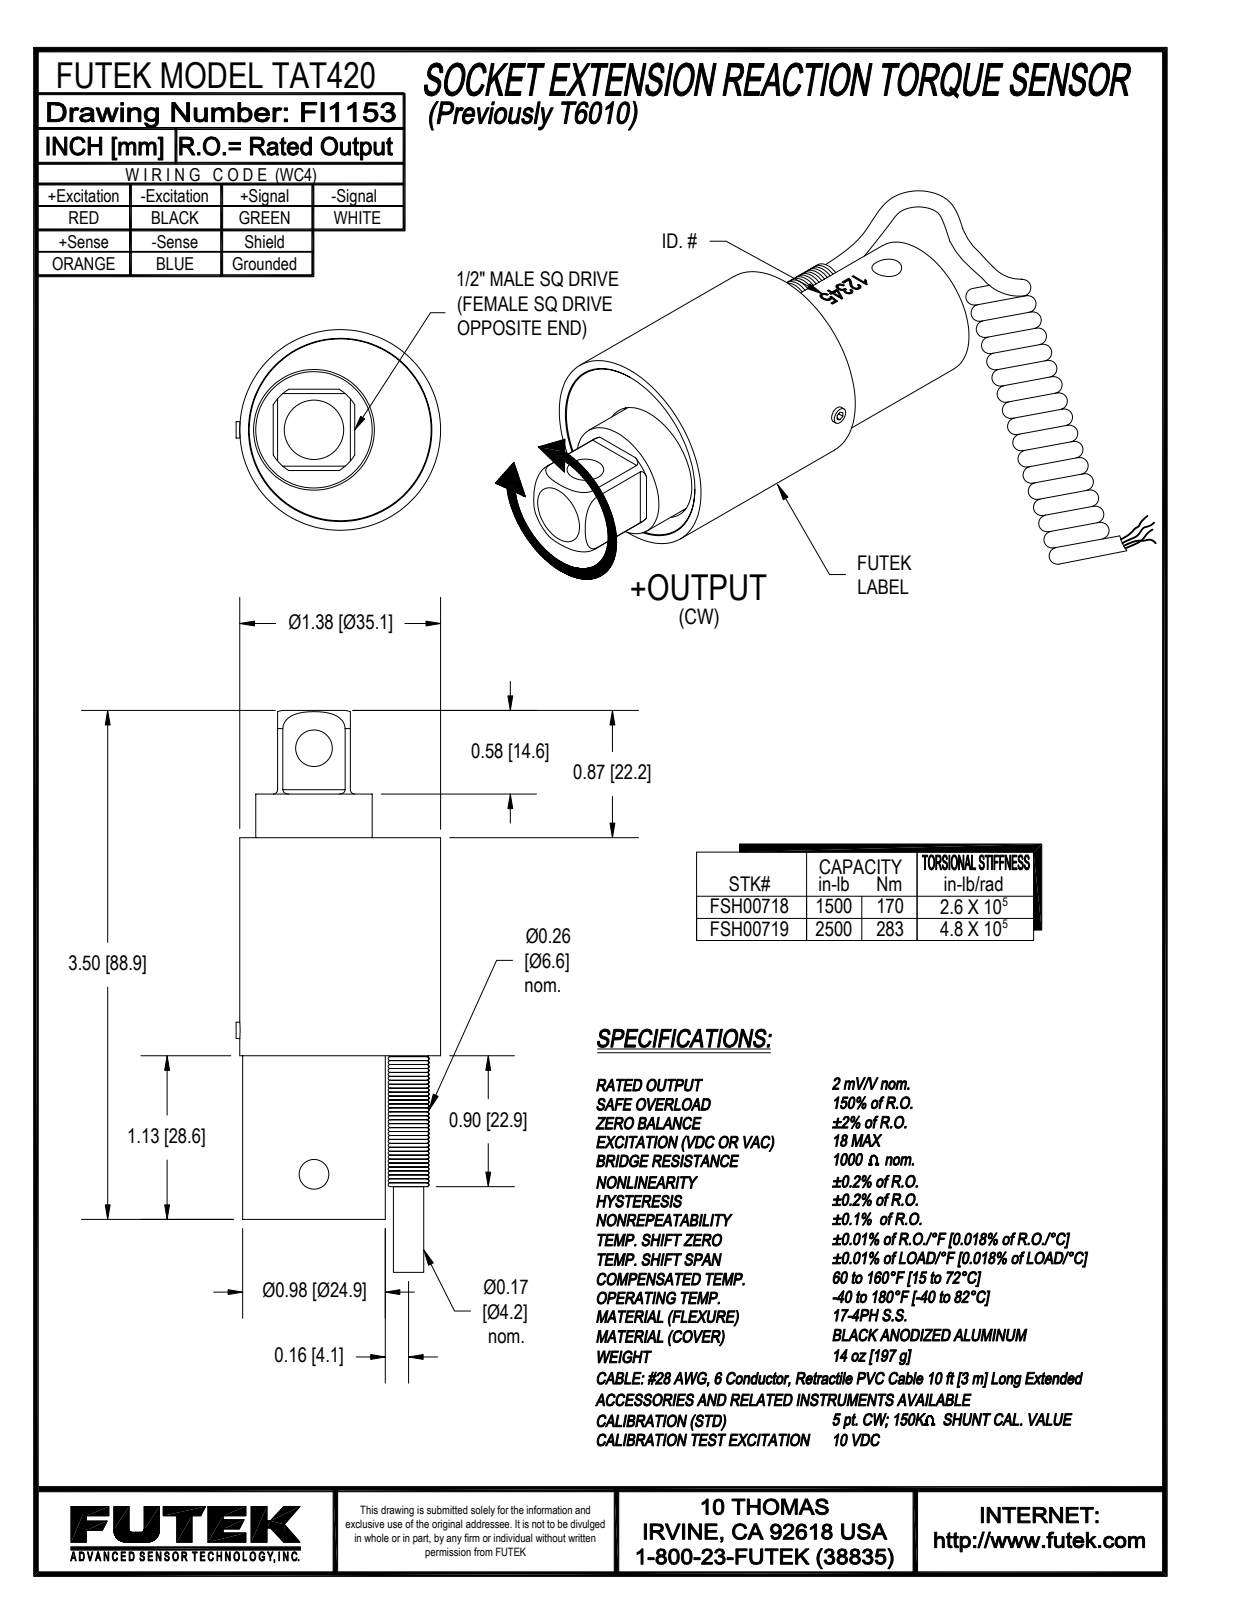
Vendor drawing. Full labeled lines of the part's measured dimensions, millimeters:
Part name (STEP PRODUCT): TAT420 (SubstituteLevelofDetail1); TAT420_Substitute_1
STEP written by: Autodesk Inventor 2011 (AUTOMOTIVE_DESIGN)
Units: millimetres
Bodies: 2 solids, 101 faces (33 planar, 23 cylindrical, 45 other)
Overall size (bounding box): 89.5 × 35.7 × 35.1
Volume: 41 200 mm³ · Surface area: 19 260 mm²
Round holes (diameter × count): ⌀3.3 ×1, ⌀5.1 ×1, ⌀5.2 ×1, ⌀6.4 ×1, ⌀21.1 ×1, ⌀21.8 ×1, ⌀31.2 ×1, ⌀32 ×1
Round bosses / shafts (diameter × count): ⌀35.1 ×1, ⌀31.8 ×1, ⌀24.9 ×1, ⌀21.7 ×1, ⌀20.3 ×1, ⌀5.8 ×1, ⌀2.8 ×1
Partial cylindrical surfaces — rounded edges, fillets, slot ends (radius × count): R0.8 ×1, R8.4 ×1
Main face-to-face distances: 38, 34.9, 3, 8.9, 26, 29.1, 12.8, 12.7, 63.5, 28.6
Hole centre spacings: 4.6, 11.9, 16.5, 74.4
